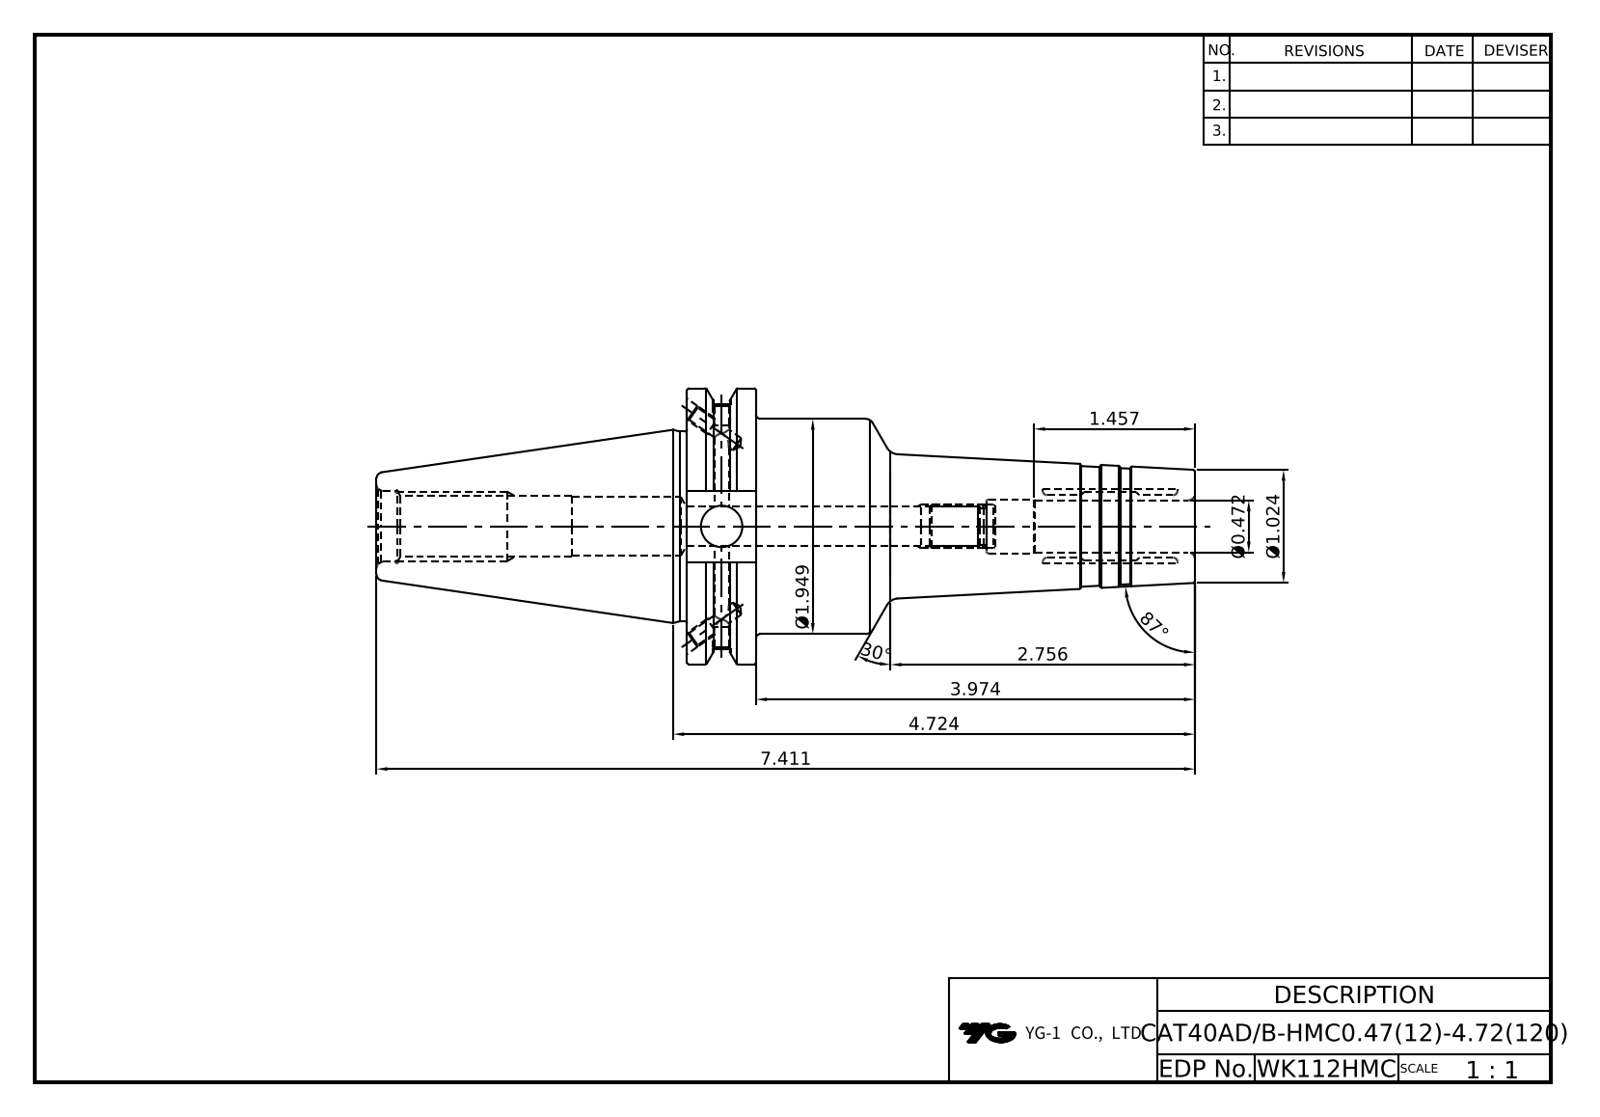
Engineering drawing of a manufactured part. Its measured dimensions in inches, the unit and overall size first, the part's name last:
Units: inches
Overall size (bounding box): 7.411 × 2.5 × 2.405
Round holes (diameter × count): ⌀0.128 ×4, ⌀0.157 ×2, ⌀0.165 ×2, ⌀0.351 ×1, ⌀0.375 ×1, ⌀0.472 ×1, ⌀0.496 ×1, ⌀0.512 ×1, ⌀0.527 ×1, ⌀0.642 ×1
Round bosses / shafts (diameter × count): ⌀2.5 ×1, ⌀1.949 ×1, ⌀1.717 ×1
Partial cylindrical surfaces — rounded edges, fillets, slot ends (radius × count): R0.322 ×1, R1.108 ×1
Main face-to-face distances: 0.625, 4.6, 3.974, 1.874, 0.645, 2.812, 3.437, 7.411, 3.05, 0.238
Volume: 11.88 in³ · Surface area: 52.85 in²
Bodies: 1 solid, 106 faces (36 planar, 30 cylindrical, 40 other)
Part name (STEP PRODUCT): LO-CAT40ADB-HMC12-120
STEP written by: Autodesk Inventor 2020 (AUTOMOTIVE_DESIGN)
